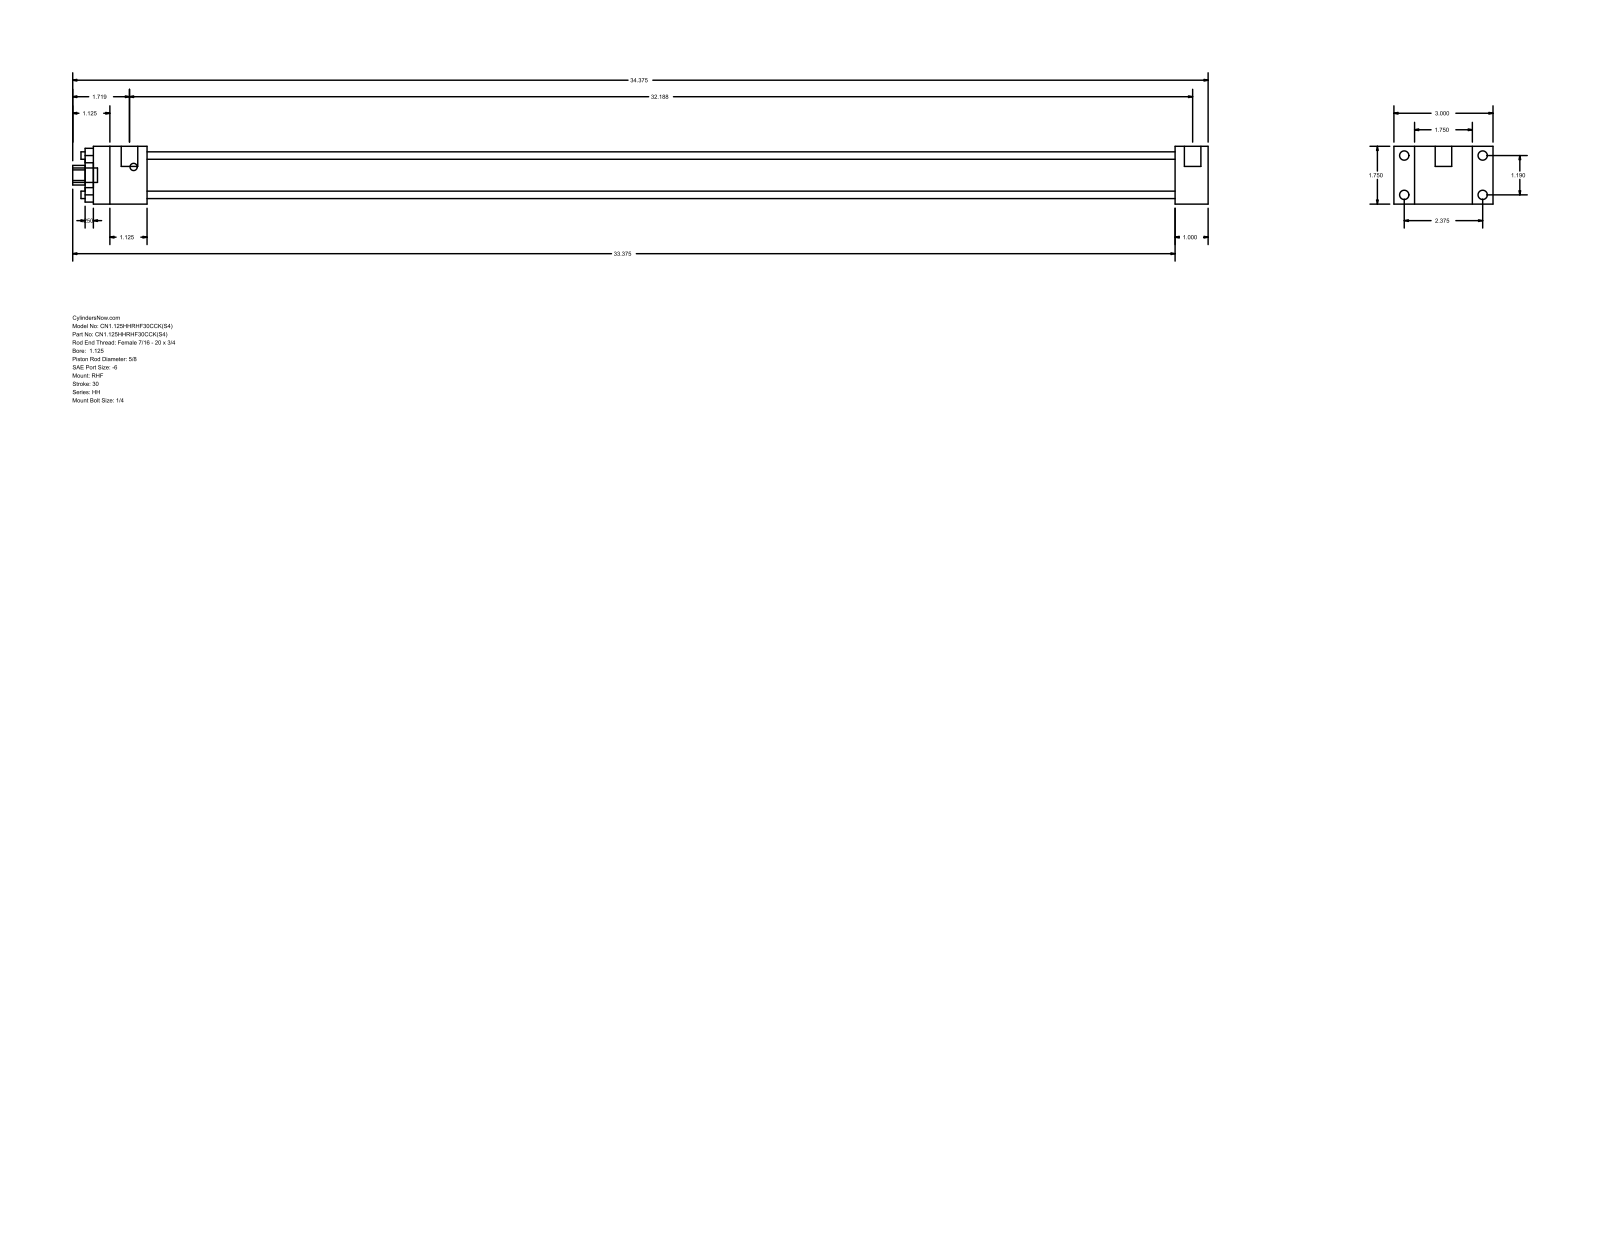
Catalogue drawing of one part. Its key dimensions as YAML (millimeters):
part_name: "HH_RHF__0112_0.625"
step_written_by: "GSSL Pune (CONFIG_CONTROL_DESIGN)"
units: millimeters
bodies: {solids: 0, faces: 88, planar: 60, cylindrical: 28, other: 0}
overall_size: [873.12, 76.2, 44.45]
round_holes:
  - {diameter: 5.71, count: 4}
  - {diameter: 15.88, count: 1}
  - {diameter: 28.57, count: 1}
  - {diameter: 34.92, count: 1}
round_bosses_or_shafts:
  - {diameter: 7.14, count: 4}
  - {diameter: 5.56, count: 4}
  - {diameter: 12.7, count: 2}
  - {diameter: 11.11, count: 1}
partial_cylinders:
  - {radius: 7.54, count: 1}
face_to_face_distances: [44.46, 15.87, 60.33, 25.39, 76.2, 790.58, 815.97, 41.27, 831.85, 857.24]
hole_center_spacings: [21.37, 30.22, 42.74]
